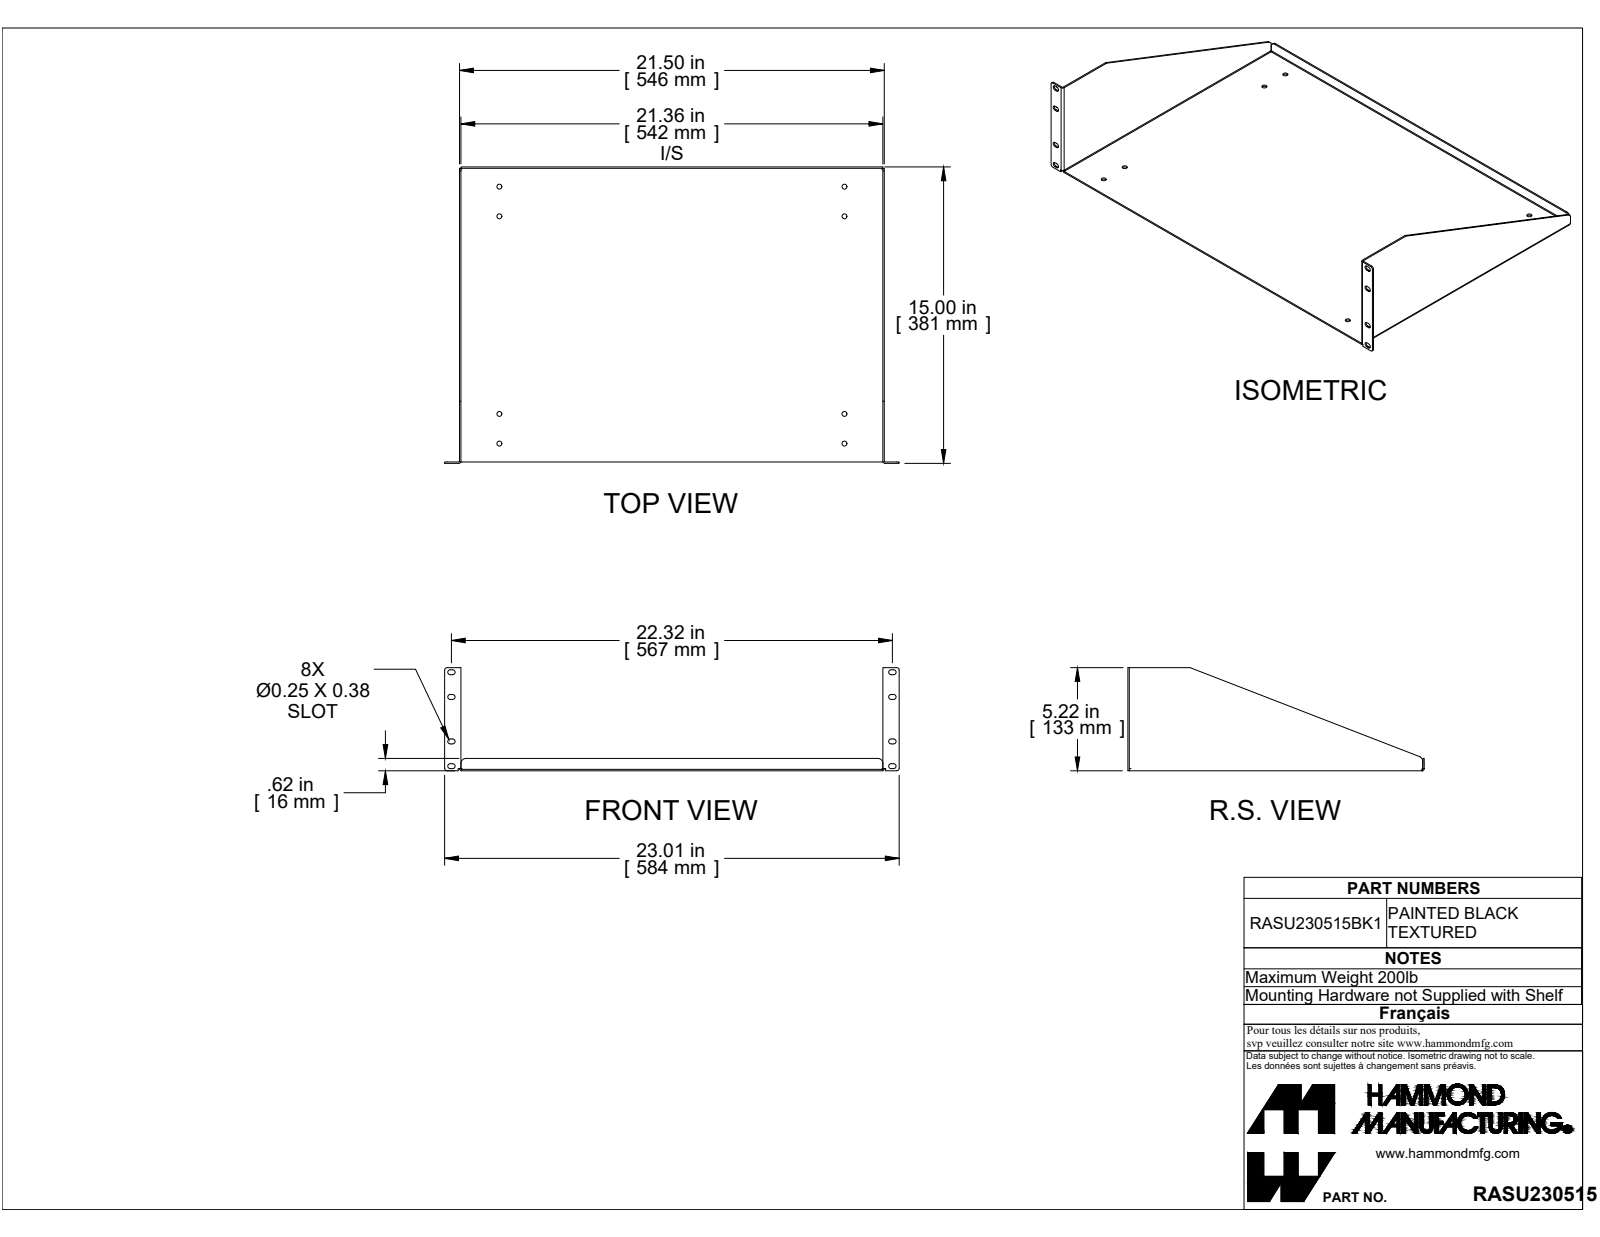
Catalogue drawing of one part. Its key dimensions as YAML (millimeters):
part_name: "RASU230515BK1"
step_written_by: "SolidWorks 2019 (CONFIG_CONTROL_DESIGN)"
units: millimeters
bodies: {solids: 1, faces: 104, planar: 56, cylindrical: 44, other: 4}
overall_size: [584.4, 381, 132.5]
volume: 516200
surface_area: 569400
round_holes:
  - {diameter: 6.4, count: 8}
partial_cylinders:
  - {radius: 3.2, count: 20}
  - {radius: 0.9, count: 5}
  - {radius: 2.7, count: 5}
  - {radius: 1.4, count: 3}
  - {radius: 6.4, count: 2}
face_to_face_distances: [1.8, 544.3, 542.4, 546.1, 377.3, 379.2, 1.8, 379.2, 381, 15.9]
hole_center_spacings: [38.1, 292.1, 443.7, 445.3, 531.2, 254, 330.2, 511.3]
